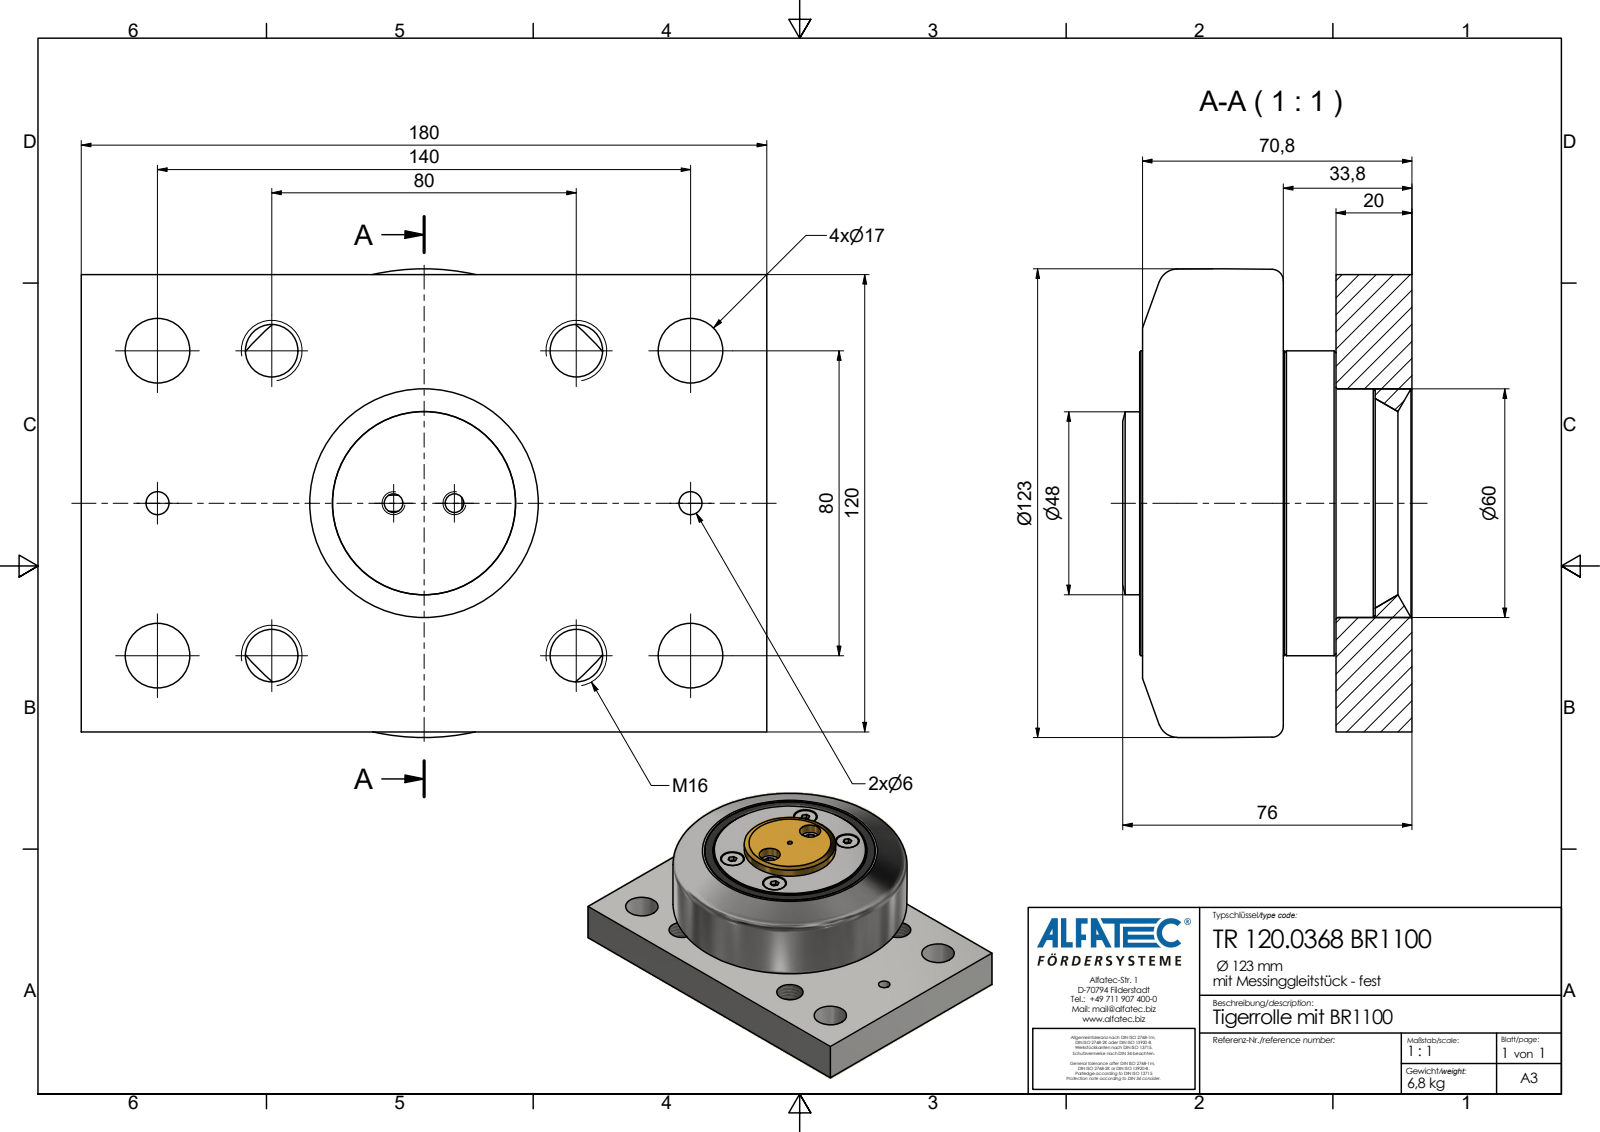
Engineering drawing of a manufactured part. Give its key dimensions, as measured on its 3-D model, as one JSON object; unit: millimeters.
{"part_name": "TR 120.0368 BR1100_Kontur", "step_written_by": "Autodesk Inventor 2020 (AP242_MANAGED_MODEL_BASED_3D_ENGINEERING_MIM_LF)", "units": "millimeters", "bodies": {"solids": 1, "faces": 101, "planar": 66, "cylindrical": 25, "other": 10}, "overall_size": [180, 123, 76], "volume_mm3": 902638, "surface_area_mm2": 90943, "round_holes": [[12.4, 4], [13.84, 4], [17, 4], [6, 2], [11, 2], [2.5, 1]], "round_bosses_or_shafts": [[11.7, 4], [80, 1], [48, 1]], "face_to_face_distances": [20, 33.8, 13.8, 120, 71.5, 51.5, 37.7, 180, 70.8, 50.8], "hole_center_spacings": [31.24, 80, 30, 19.73, 27.6, 40, 44.87, 47.17]}
